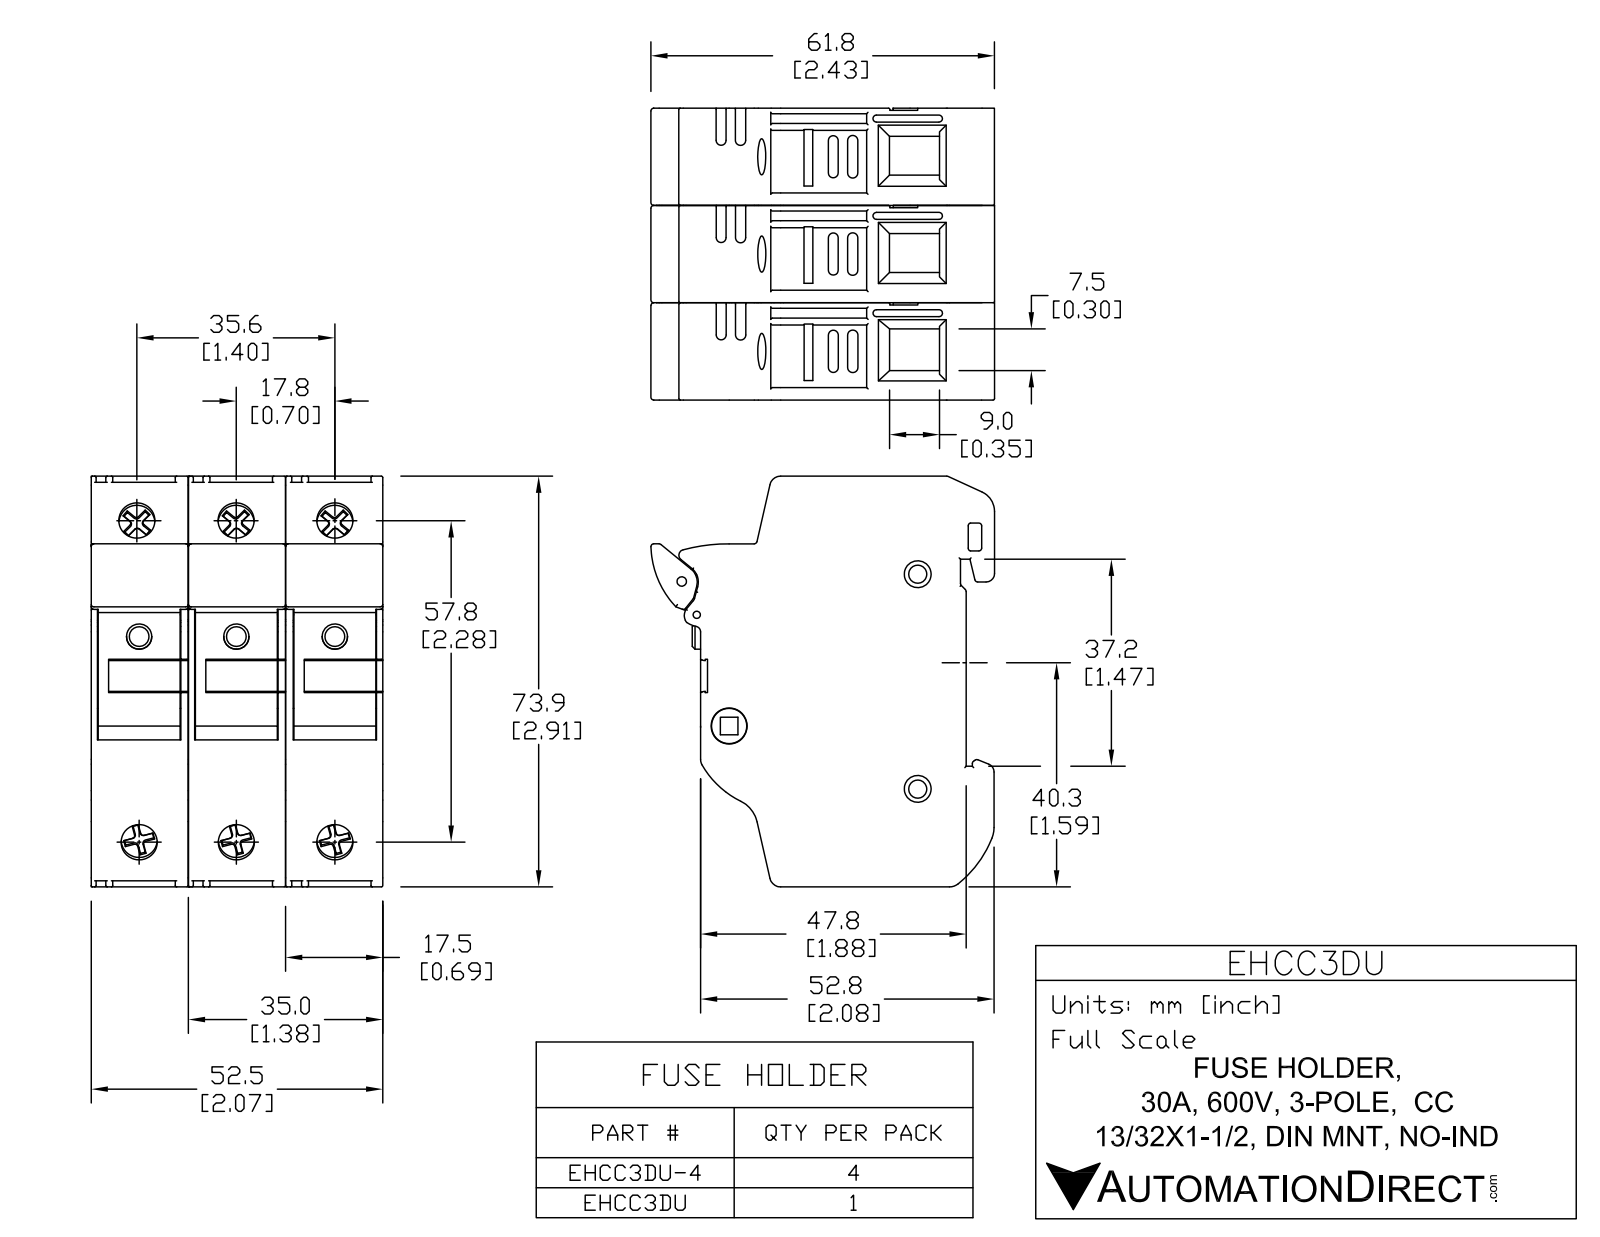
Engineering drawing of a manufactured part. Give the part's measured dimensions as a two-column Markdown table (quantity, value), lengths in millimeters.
| quantity | value |
| --- | --- |
| part name | EHCC3DU |
| STEP written by | SolidWorks 2011 (AUTOMOTIVE_DESIGN) |
| units | millimeters |
| bodies | 1 solid, 1558 faces (742 planar, 502 cylindrical, 314 other) |
| overall size | 73.88 × 61.82 × 52.52 |
| volume | 158 177 mm³ |
| surface area | 48 287 mm² |
| round holes (diameter × count) | 6.5 × 6, 3.25 × 2, 4.83 × 2, 1.3 × 1, 1.7 × 1, 6.48 × 1 |
| round bosses / shafts (diameter × count) | 6.35 × 1 |
| partial cylindrical surfaces (radius × count) | 0.25 × 141, 0.62 × 12, 0.5 × 11, 2 × 10, 0.51 × 9, 0.89 × 9, 0.92 × 9, 0.75 × 7 |
| main face-to-face distances | 17.5, 35, 52.5, 1.25, 1.58, 16.25, 27.51, 29.09, 22.94, 24.71 |
| hole center spacings | 17.51, 35.02, 6.58, 20.83, 27.36, 35.77, 35.79, 38.61 |
